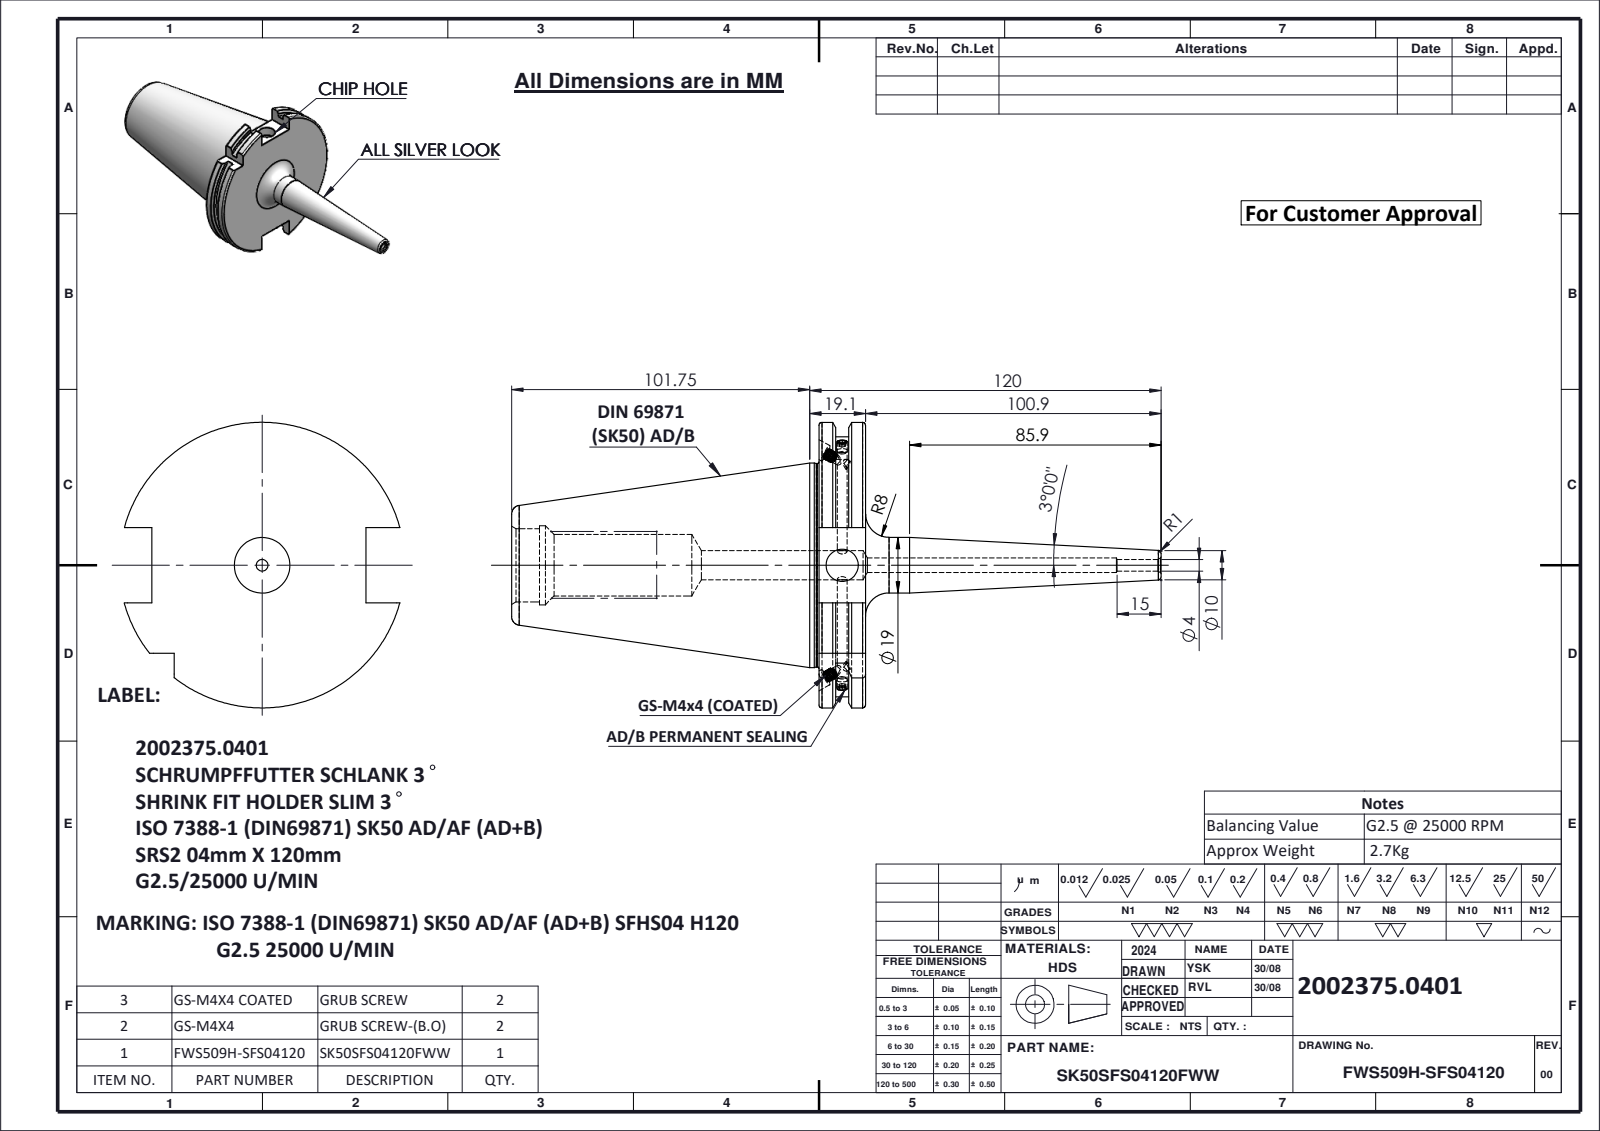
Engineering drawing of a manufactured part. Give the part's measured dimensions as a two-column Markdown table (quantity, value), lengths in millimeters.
| quantity | value |
| --- | --- |
| part name | FWS509H-SFS04120; GS-M4X4_DIN 913 - M4 x 4-N; SK50SFS04120FWW; GS-M4X4-COATING_DIN 913 - M4 x 4-N |
| STEP written by | SolidWorks 2024 (CONFIG_CONTROL_DESIGN) |
| units | millimeters |
| bodies | 5 solids, 254 faces (61 planar, 75 cylindrical, 118 other) |
| overall size | 221.75 × 97.5 × 94.05 |
| volume | 351 495 mm³ |
| surface area | 49 711 mm² |
| round holes (diameter × count) | 3.2 × 2, 6 × 2, 3.3 × 1, 4 × 1, 5 × 1, 10 × 1, 11 × 1, 21 × 1, 25 × 1, 27 × 1 |
| round bosses / shafts (diameter × count) | 4 × 4, 2.9 × 2, 69.85 × 1, 69.45 × 1, 19 × 1 |
| partial cylindrical surfaces (radius × count) | 44.9 × 1, 48.75 × 1 |
| main face-to-face distances | 15.9, 5.65, 10.25, 10.14, 4.49, 5.76, 104.95, 110.6, 115.09, 120.85 |
